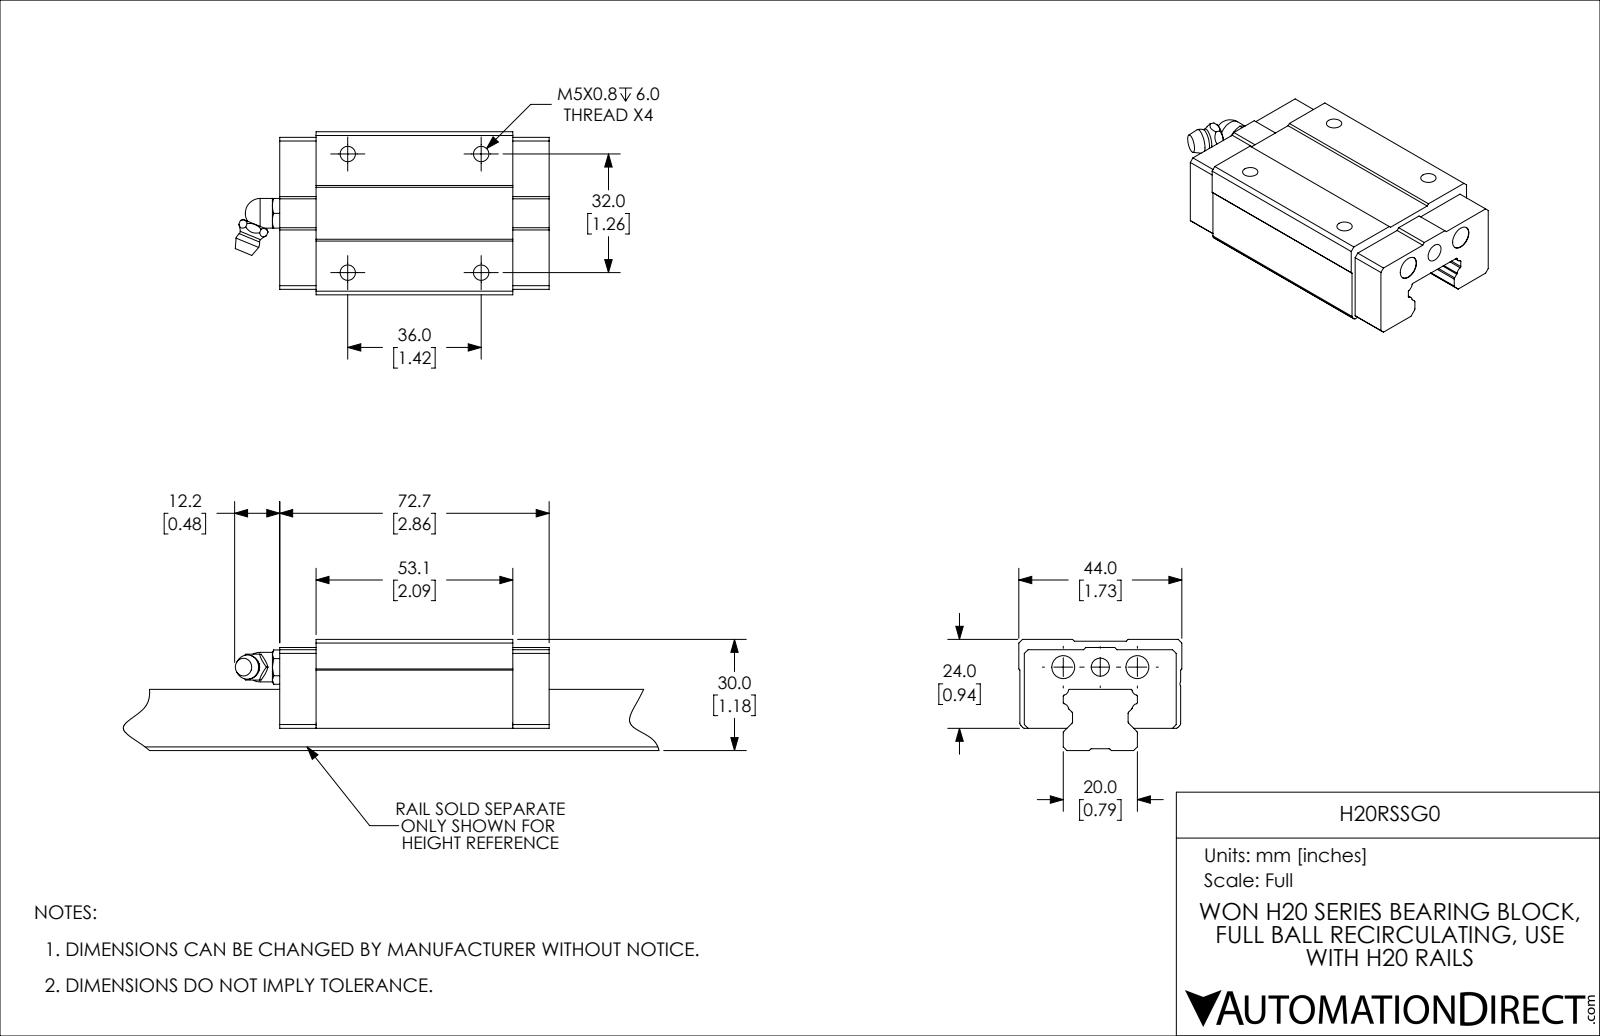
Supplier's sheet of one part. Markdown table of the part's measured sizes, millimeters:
| quantity | value |
| --- | --- |
| part name | H20RSSG0 |
| STEP written by | SolidWorks 2019 (CONFIG_CONTROL_DESIGN) |
| units | millimeters |
| bodies | 2 solids, 150 faces (75 planar, 45 cylindrical, 30 other) |
| overall size | 84.7 × 44 × 24 |
| volume | 59 262 mm³ |
| surface area | 14 097 mm² |
| round holes (diameter × count) | 4.13 × 4, 6.2 × 2, 4.92 × 1 |
| round bosses / shafts (diameter × count) | 8 × 1, 6 × 1 |
| partial cylindrical surfaces (radius × count) | 0.5 × 8, 1 × 5, 0.3 × 4, 1.6 × 4 |
| main face-to-face distances | 10.5, 24, 13.5, 13, 1.2, 42.2, 23.5, 0.5, 1.5, 42.5 |
| hole center spacings | 10, 32, 36, 48.17, 20 |
